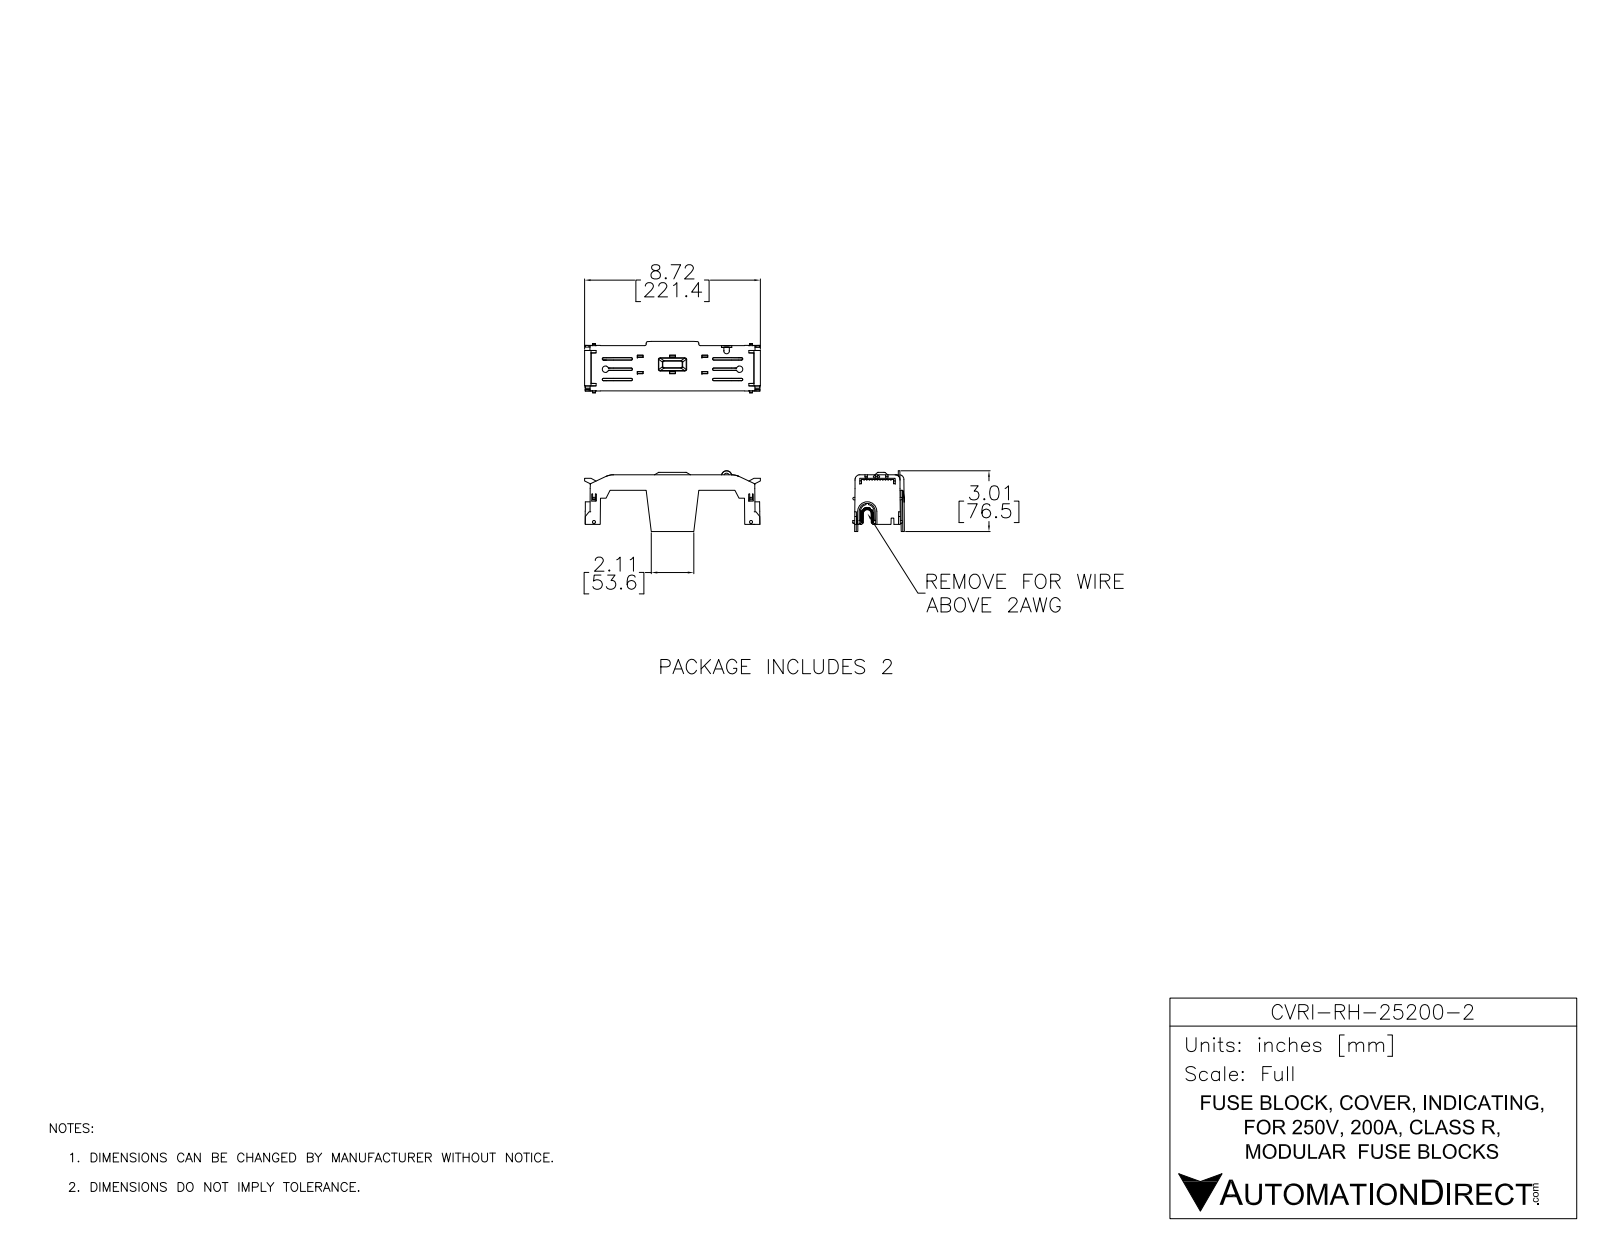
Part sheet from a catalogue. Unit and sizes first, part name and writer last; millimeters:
Units: millimetres
Overall size (bounding box): 221.4 × 76.5 × 64.9
Round holes (diameter × count): ⌀7 ×1
Partial cylindrical surfaces — rounded edges, fillets, slot ends (radius × count): R1 ×16, R6 ×9, R3 ×8, R4 ×7, R2 ×6, R0.3 ×2, R0.5 ×2, R16 ×2
Main face-to-face distances: 2, 5, 3, 7, 20.4, 15.3, 42.2, 44.2, 32.7, 34.7
Volume: 75 660 mm³ · Surface area: 80 650 mm²
Bodies: 1 solid, 1406 faces (950 planar, 105 cylindrical, 351 other)
Part name (STEP PRODUCT): CVRI-RH-25200-2
STEP written by: SolidWorks 2017 (AUTOMOTIVE_DESIGN)
